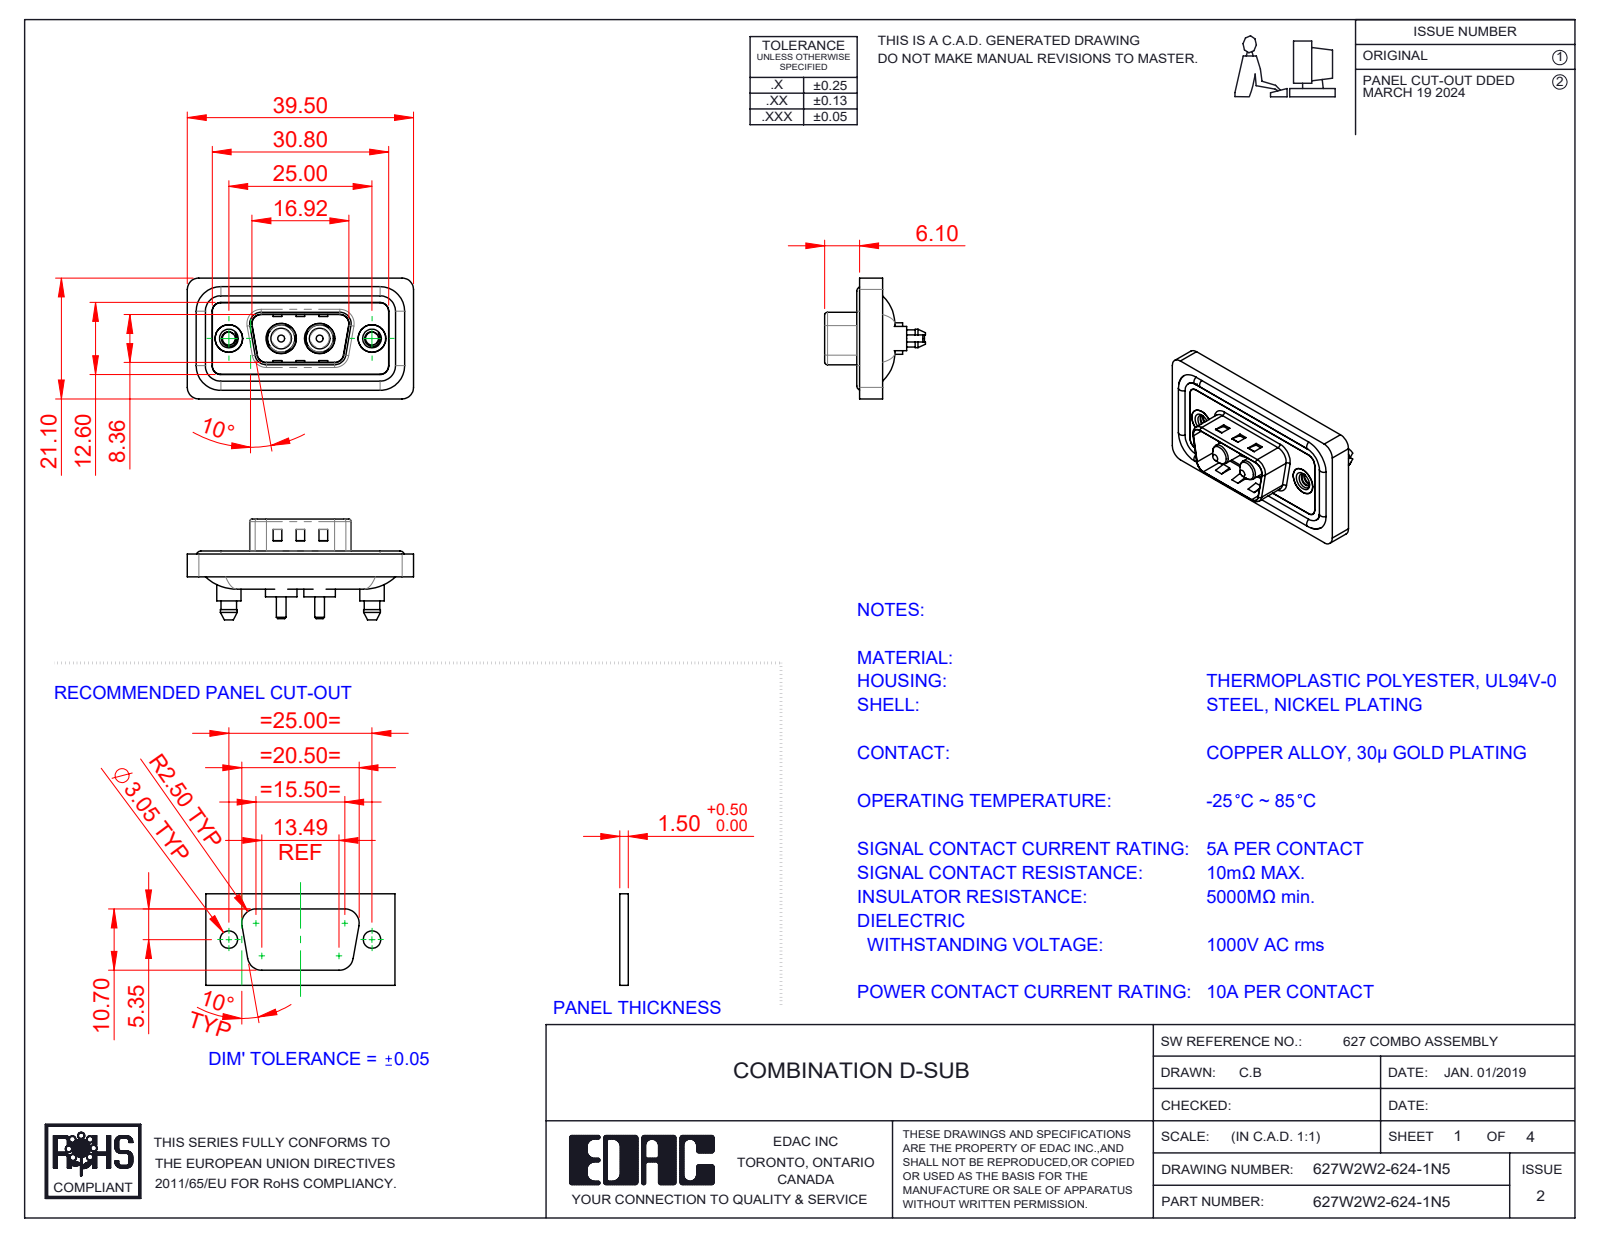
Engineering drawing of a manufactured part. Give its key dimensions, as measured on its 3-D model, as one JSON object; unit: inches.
{"part_name": "627Combo Threaded Boardlock_5; 627Combo Shell Rear_09 Contacts; 627W2W2-624-1N5; 627Combo Housing_2W2 (+3 more)", "step_written_by": "SolidWorks 2023 (CONFIG_CONTROL_DESIGN)", "units": "inches", "bodies": {"solids": 11, "faces": 539, "planar": 181, "cylindrical": 250, "other": 108}, "overall_size": [1.555, 0.831, 0.693], "volume_in3": 0.279, "surface_area_in2": 11.3, "round_holes": [[0.089, 2], [0.157, 2], [0.189, 2], [0.191, 2], [0.197, 2], [0.209, 2]], "round_bosses_or_shafts": [[0.063, 4], [0.217, 2], [0.213, 2], [0.205, 2], [0.193, 2], [0.187, 2], [0.167, 2], [0.148, 2]], "partial_cylinders_radius": [[0.059, 24], [0.079, 18], [0.063, 10], [0.02, 8], [0.01, 4], [0.024, 4], [0.026, 4], [0.035, 4]], "face_to_face_distances": [0.016, 0.043, 0.114, 0.059, 0.122, 0.02, 0.063, 0.157, 0.028, 0.098], "hole_center_spacings": [0.36, 0.624, 0.265, 0.984]}
